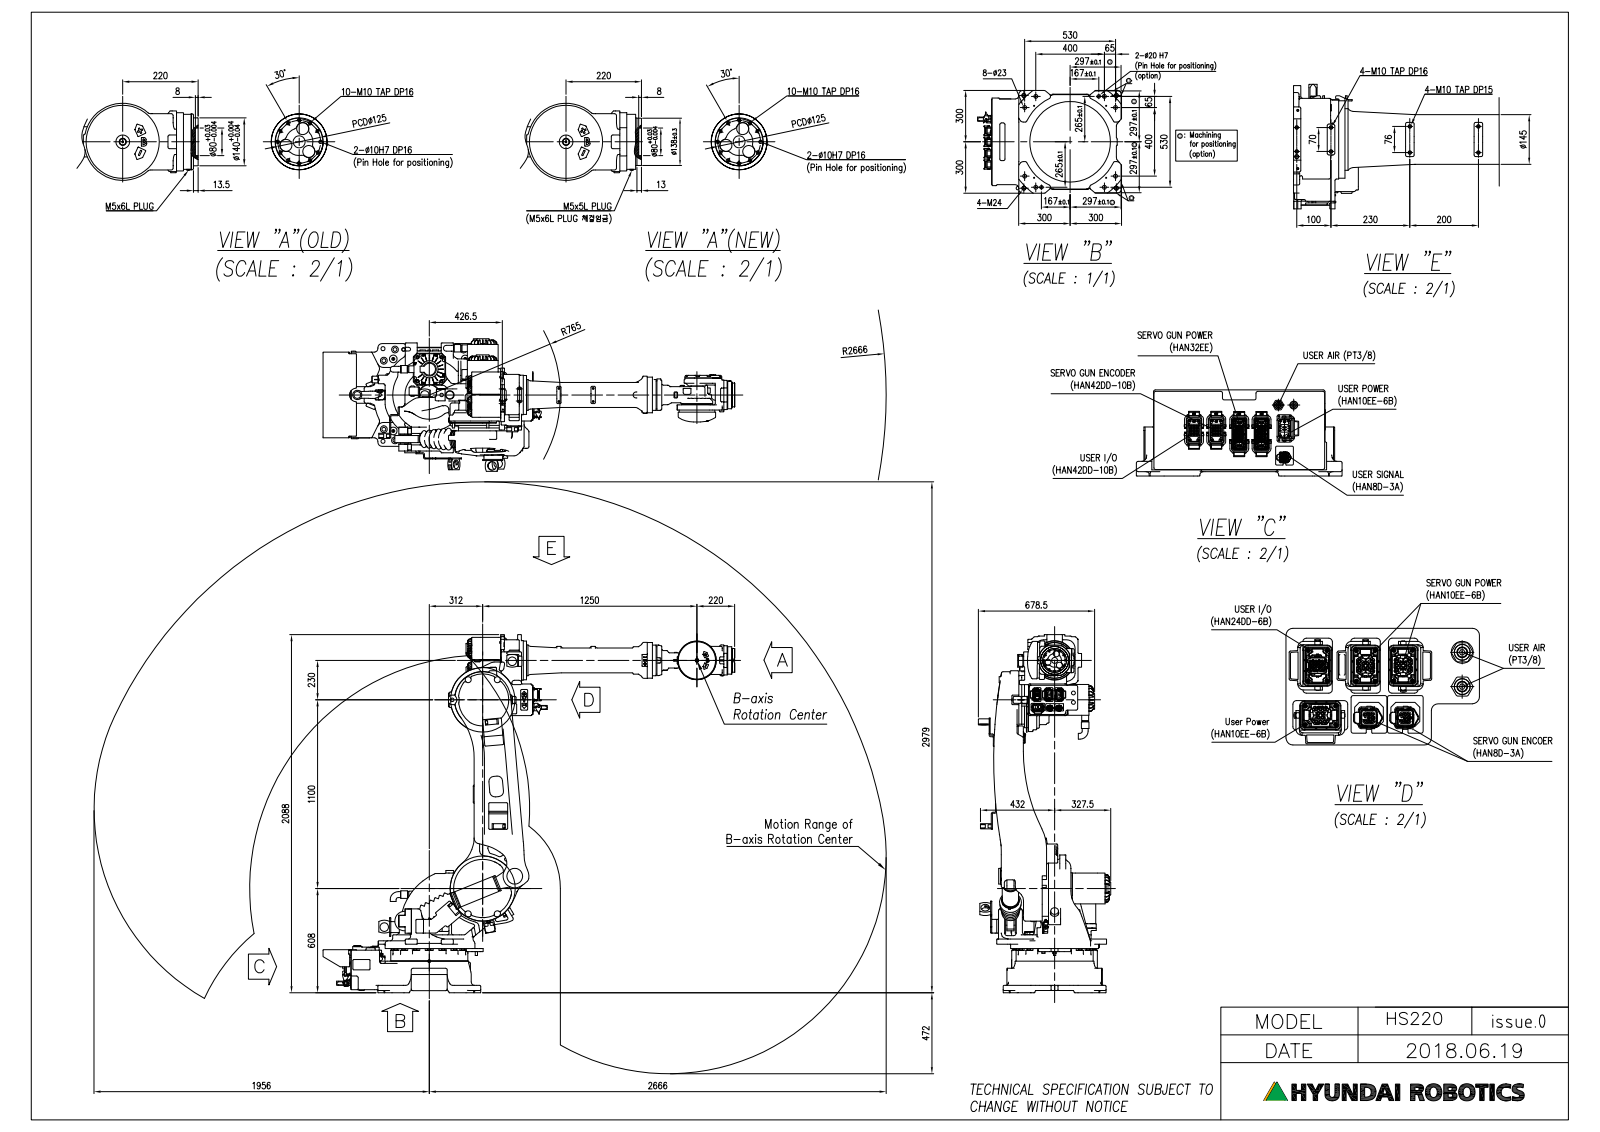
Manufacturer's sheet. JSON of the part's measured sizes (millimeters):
{"part_name": "HS220_GAS SPRING CYLINDER_1; HS220_S1A2 ASSY_1; HS220_S1 OUTPUT_1; HS220_BS JOINT_1 (+8 more)", "step_written_by": "SolidWorks 2017 (CONFIG_CONTROL_DESIGN)", "units": "millimeters", "bodies": {"solids": 46, "faces": 2495, "planar": 1229, "cylindrical": 885, "other": 381}, "overall_size": [2237, 2073, 683.5], "volume_mm3": 251700000, "surface_area_mm2": 10660000, "round_holes": [[10, 12], [8.5, 10], [6, 8], [35, 5], [110, 4], [30, 3], [6.8, 2], [8, 2], [40, 2], [48, 2], [64, 2], [70, 2]], "round_bosses_or_shafts": [[35, 7], [80, 4], [100, 3], [60, 3], [325, 2], [284, 2], [283.5, 2], [278.4, 2]], "partial_cylinders_radius": [[15, 35], [5, 33], [10, 25], [0.5, 16], [30, 15], [50, 8], [20, 7], [9.5, 6]], "face_to_face_distances": [30, 240, 15, 90, 10, 5, 146.5, 115.76, 101.5, 141.5], "hole_center_spacings": [62.5, 88.39, 120.74, 32.35, 64.81, 82.3, 108.25, 108.26]}
